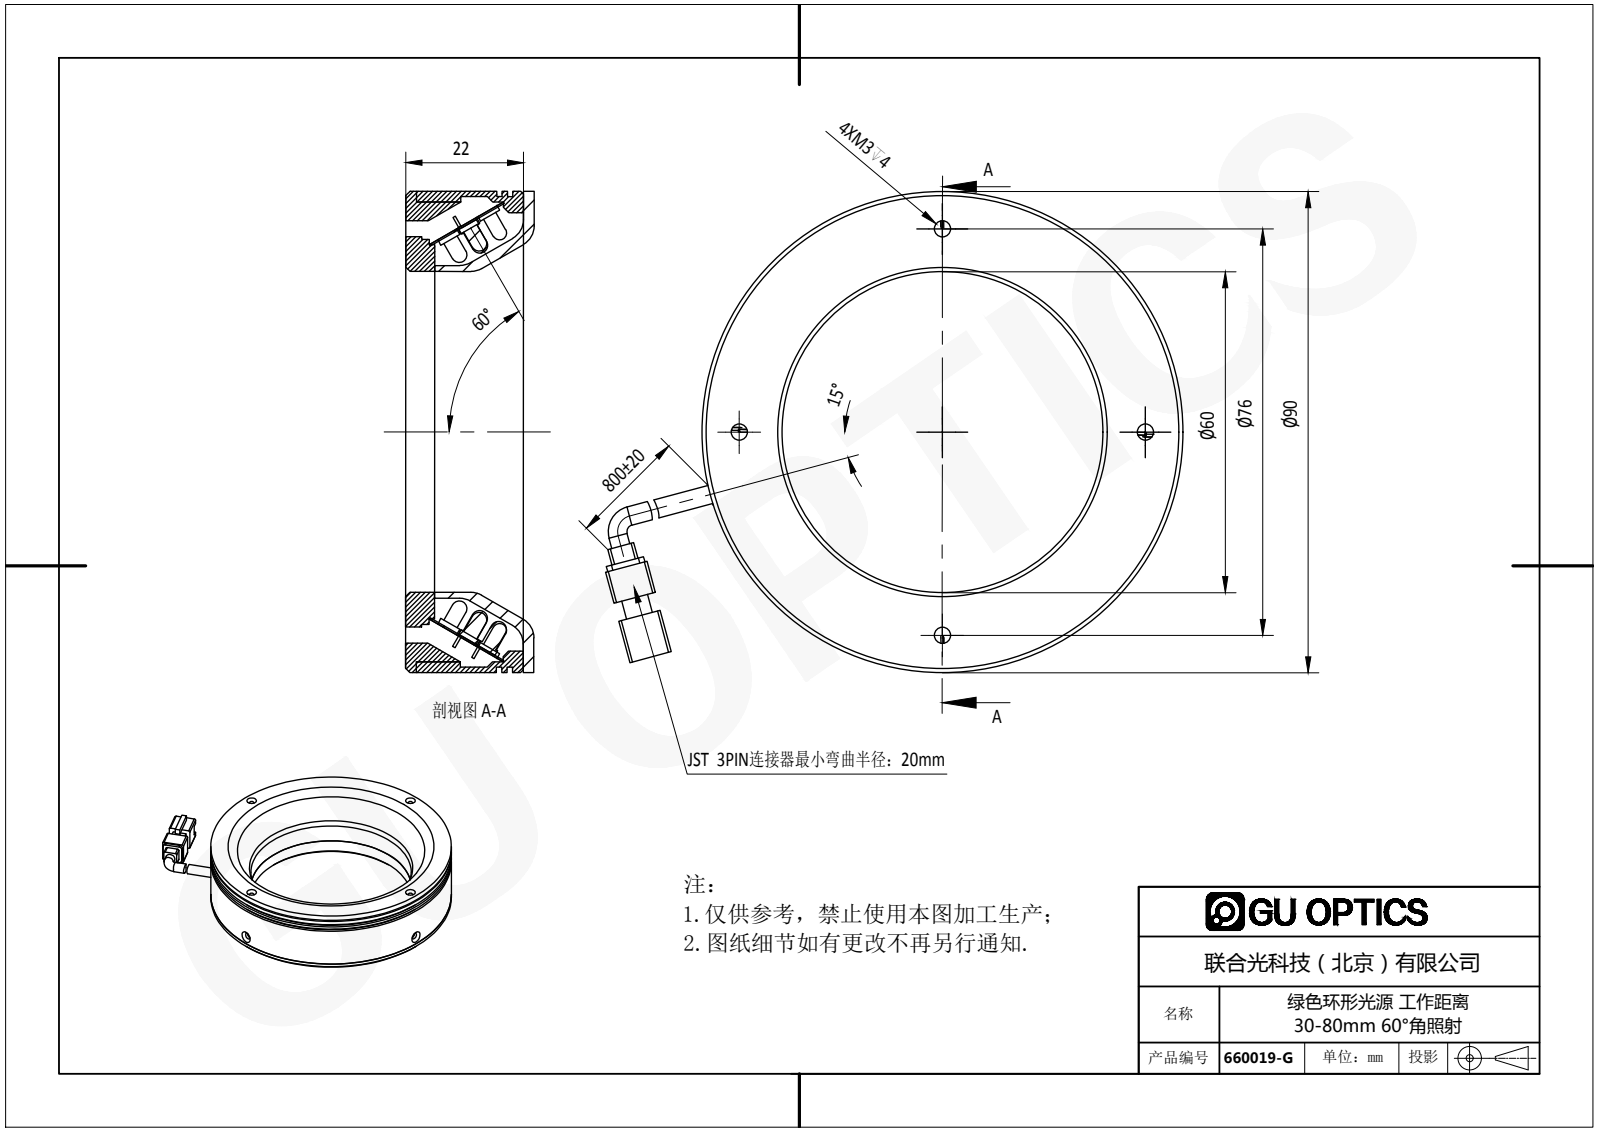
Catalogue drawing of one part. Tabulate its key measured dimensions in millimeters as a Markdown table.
| quantity | value |
| --- | --- |
| part name | 660019-G |
| STEP written by | SolidWorks 2016 (AUTOMOTIVE_DESIGN) |
| units | millimeters |
| bodies | 153 solids, 2753 faces (1844 planar, 708 cylindrical, 201 other) |
| overall size | 116.8 × 90 × 24.45 |
| volume | 46 795 mm³ |
| surface area | 61 171 mm² |
| round holes (diameter × count) | 1.25 × 4, 1.7 × 4, 3 × 4, 3.5 × 3, 2 × 2, 2.4 × 2, 60 × 1, 82 × 1, 86 × 1 |
| round bosses / shafts (diameter × count) | 3.8 × 147, 3 × 147, 3.5 × 2, 90 × 1, 88 × 1, 72 × 1, 70 × 1, 62.2 × 1 |
| partial cylindrical surfaces (radius × count) | 0.5 × 8, 1 × 4, 1.65 × 1, 5 × 1 |
| main face-to-face distances | 2, 22, 1, 24, 3, 20, 5.4, 16.6, 18.6, 3.4 |
| hole center spacings | 30.84, 73.93, 38, 42, 53.74, 59.4, 76, 84 |
